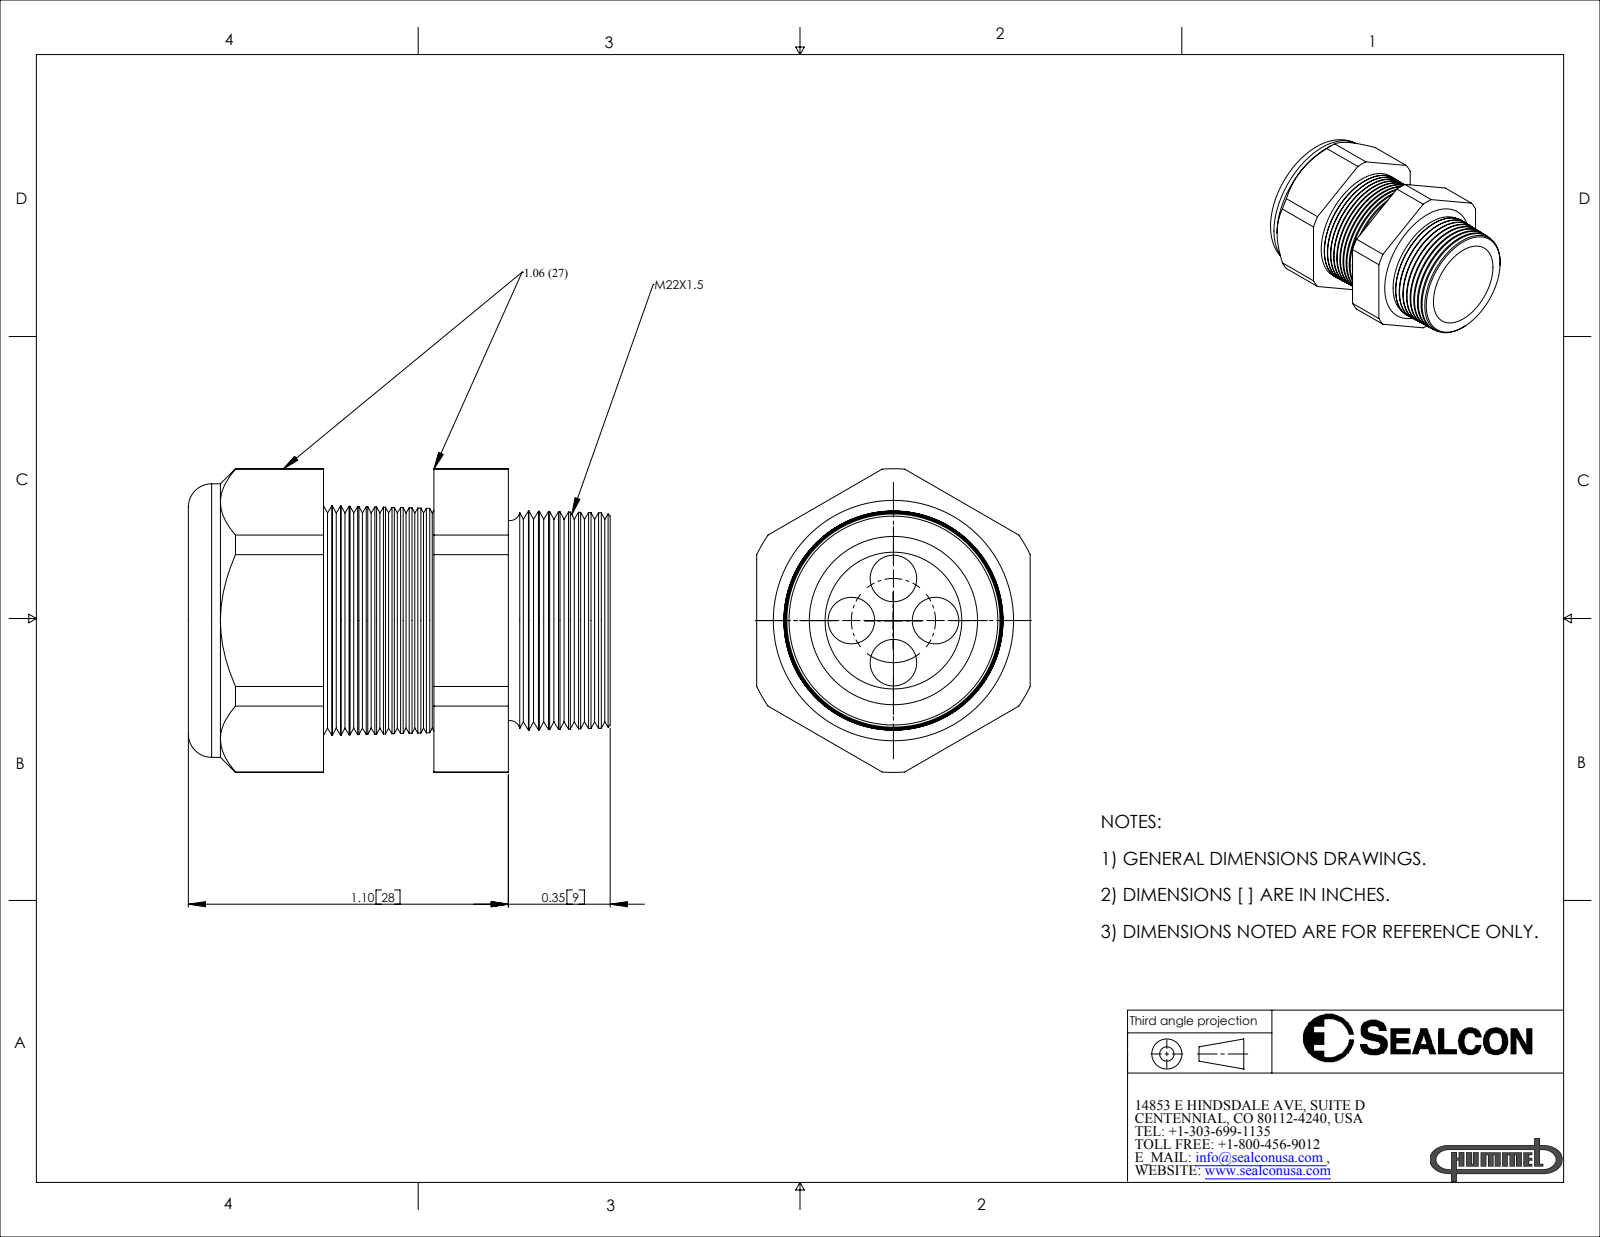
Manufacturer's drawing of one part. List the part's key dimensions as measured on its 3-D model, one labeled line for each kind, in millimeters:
Part name (STEP PRODUCT): CD22M3-BK
STEP written by: SolidWorks 2007 (CONFIG_CONTROL_DESIGN)
Units: millimetres
Bodies: 2 solids, 194 faces (20 planar, 28 cylindrical, 146 other)
Overall size (bounding box): 36.8 × 26.5 × 23.9
Volume: 9 440 mm³ · Surface area: 6 658 mm²
Round holes (diameter × count): ⌀4.1 ×4, ⌀11.4 ×1, ⌀11.9 ×1
Round bosses / shafts (diameter × count): ⌀23.9 ×1
Partial cylindrical surfaces — rounded edges, fillets, slot ends (radius × count): R13.3 ×1
Main face-to-face distances: 23.9, 21.4, 11.8, 9.7, 27.9, 16.1, 6.5, 36.8, 25, 15.4
Hole centre spacings: 3.7, 5.2, 7.3
